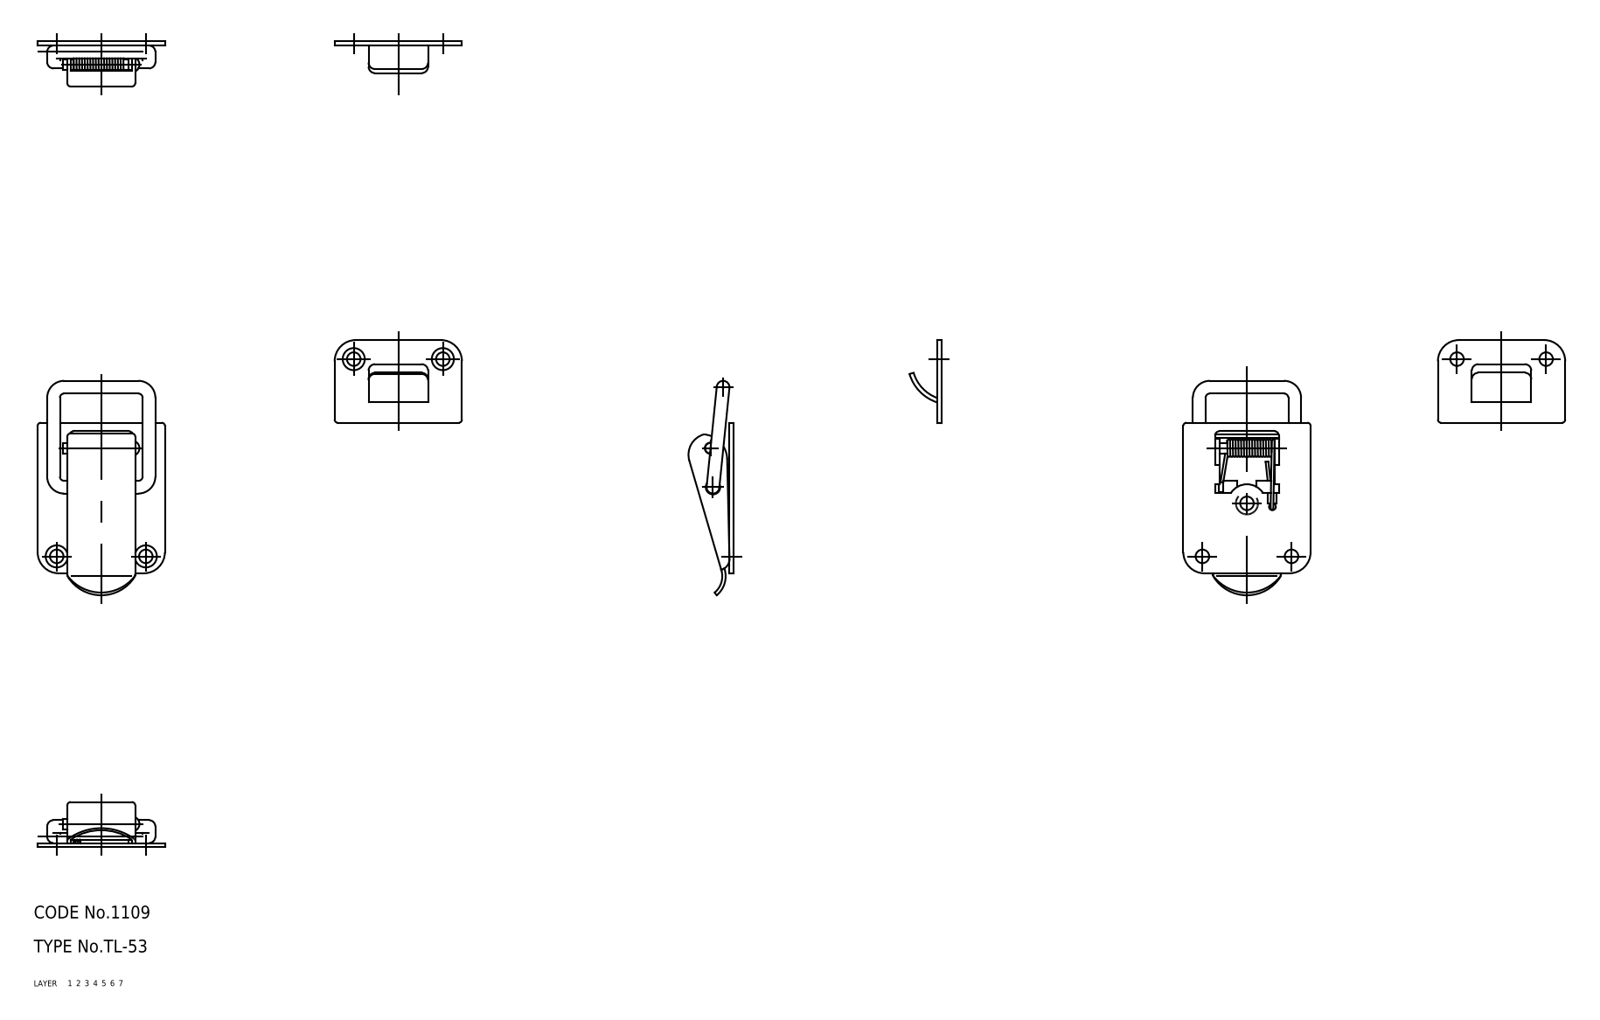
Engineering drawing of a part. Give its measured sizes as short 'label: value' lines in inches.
name: spring; shaft; lever; keeper (+3 more)
written by: CADfix (AUTOMOTIVE_DESIGN)
unit: in
bodies: 6 solids, 200 faces (0 planar, 0 cylindrical, 200 other)
size: 2.369 × 1.181 × 0.426
volume: 0.176 in³; area: 10.2 in²
